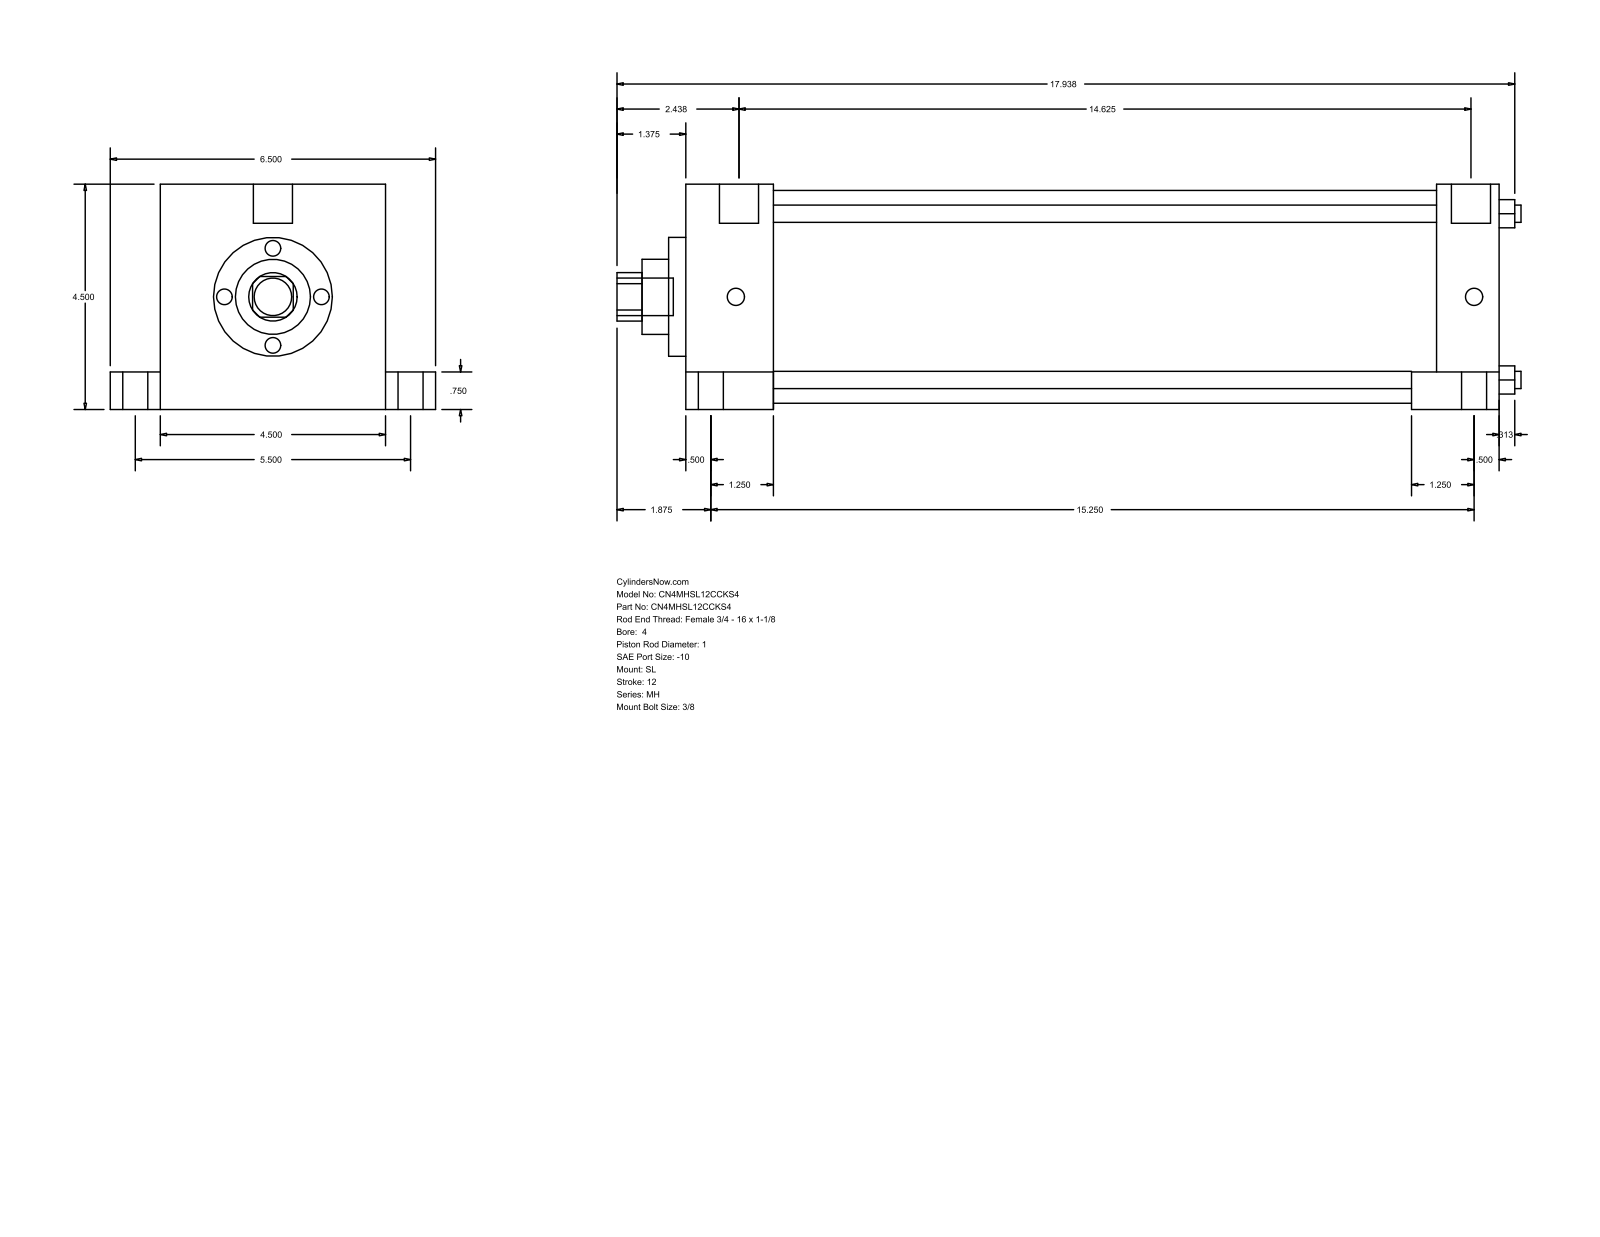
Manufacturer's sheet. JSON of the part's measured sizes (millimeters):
{"part_name": "MH_SL__0400_1", "step_written_by": "GSSL Pune (CONFIG_CONTROL_DESIGN)", "units": "millimeters", "bodies": {"solids": 0, "faces": 110, "planar": 77, "cylindrical": 33, "other": 0}, "overall_size": [458.79, 165.1, 114.3], "round_holes": [[8.76, 4], [25.4, 1], [38.1, 1], [60.33, 1], [107.95, 1]], "round_bosses_or_shafts": [[19.05, 5], [12.7, 4], [8.73, 4], [19.84, 2]], "partial_cylinders_radius": [[12.29, 1]], "face_to_face_distances": [114.3, 412.76, 44.46, 368.3, 381.01, 336.55, 31.75, 25.4, 139.7, 19.05], "hole_center_spacings": [59.62, 84.32, 119.25]}
